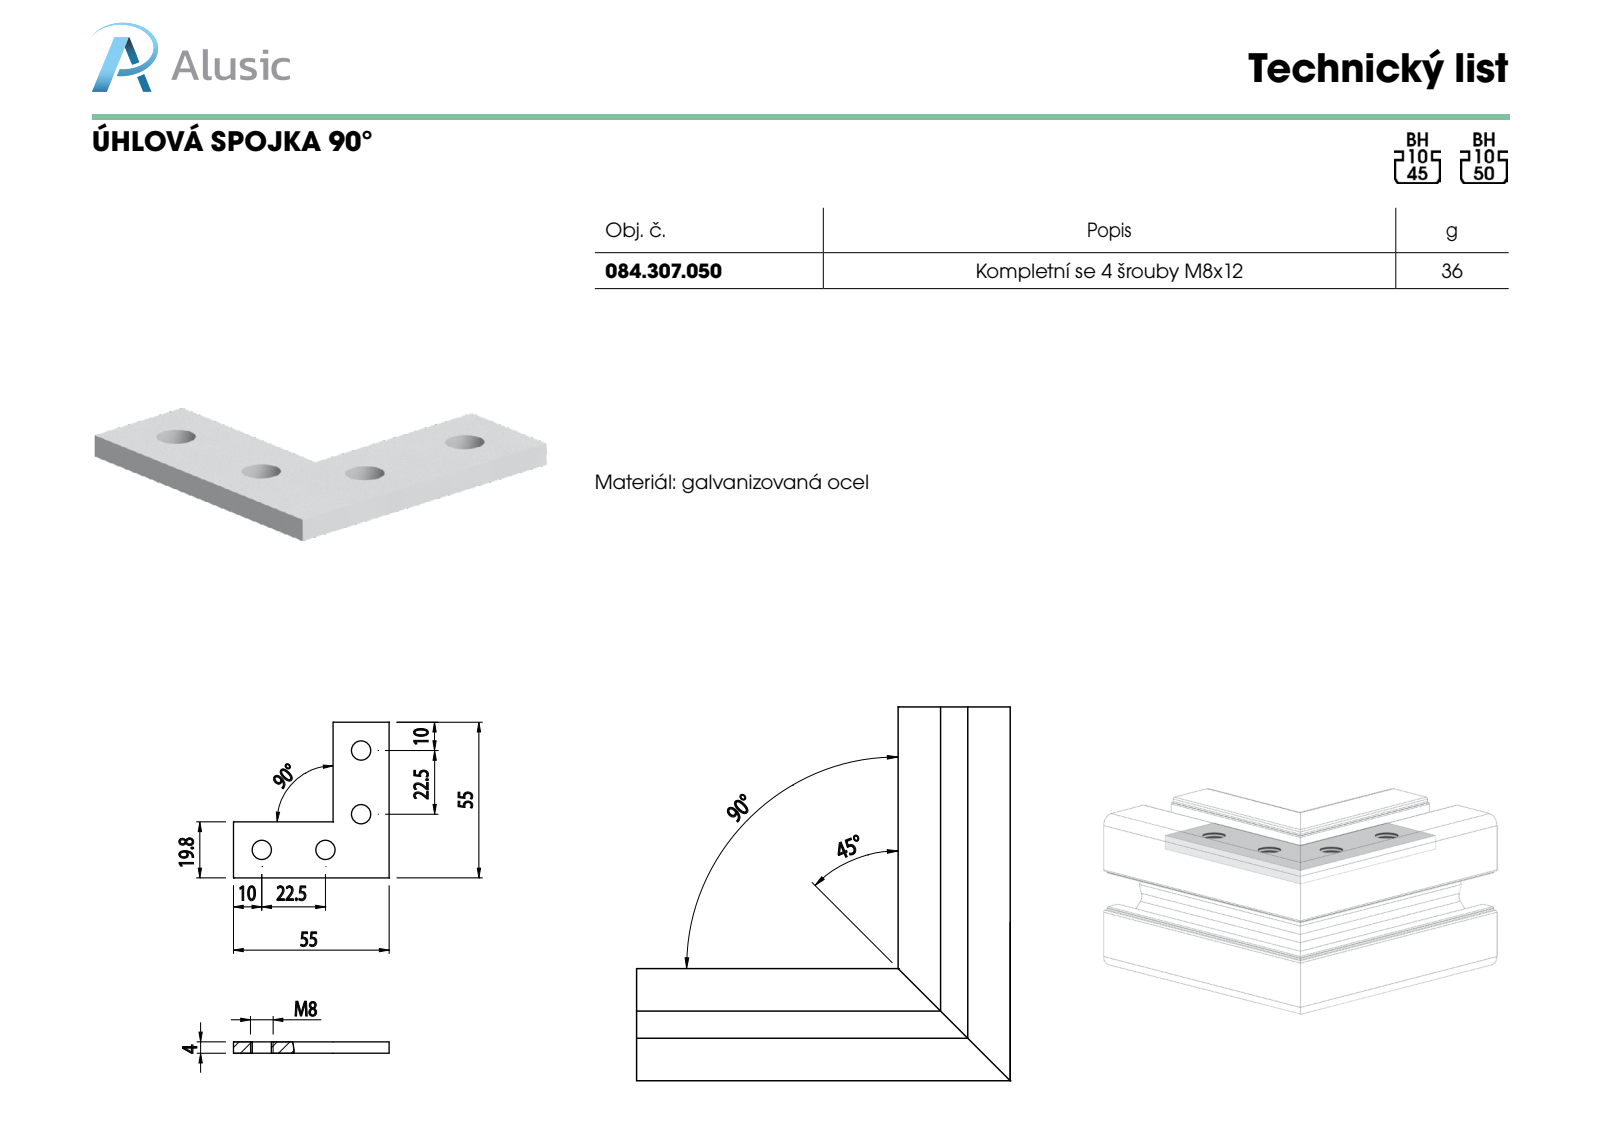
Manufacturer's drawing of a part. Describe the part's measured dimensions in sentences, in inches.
The part is named "084.307.050". Its 3-D file was written by "SolidWorks 2012 (CONFIG_CONTROL_DESIGN)". It is 1 solid with 16 faces: 8 planar, 8 cylindrical and 0 other. Overall it measures 2.165 by 2.165 by 0.157 inches. Its volume is 0.4 cubic inches and its surface area 6.98 square inches. Round holes: 4 of diameter 0.268. The main face-to-face distances are 0.157, 0.78, 1.386, 2.165. The hole center spacings are 0.886, 1.468, 0.702, 1.954.
